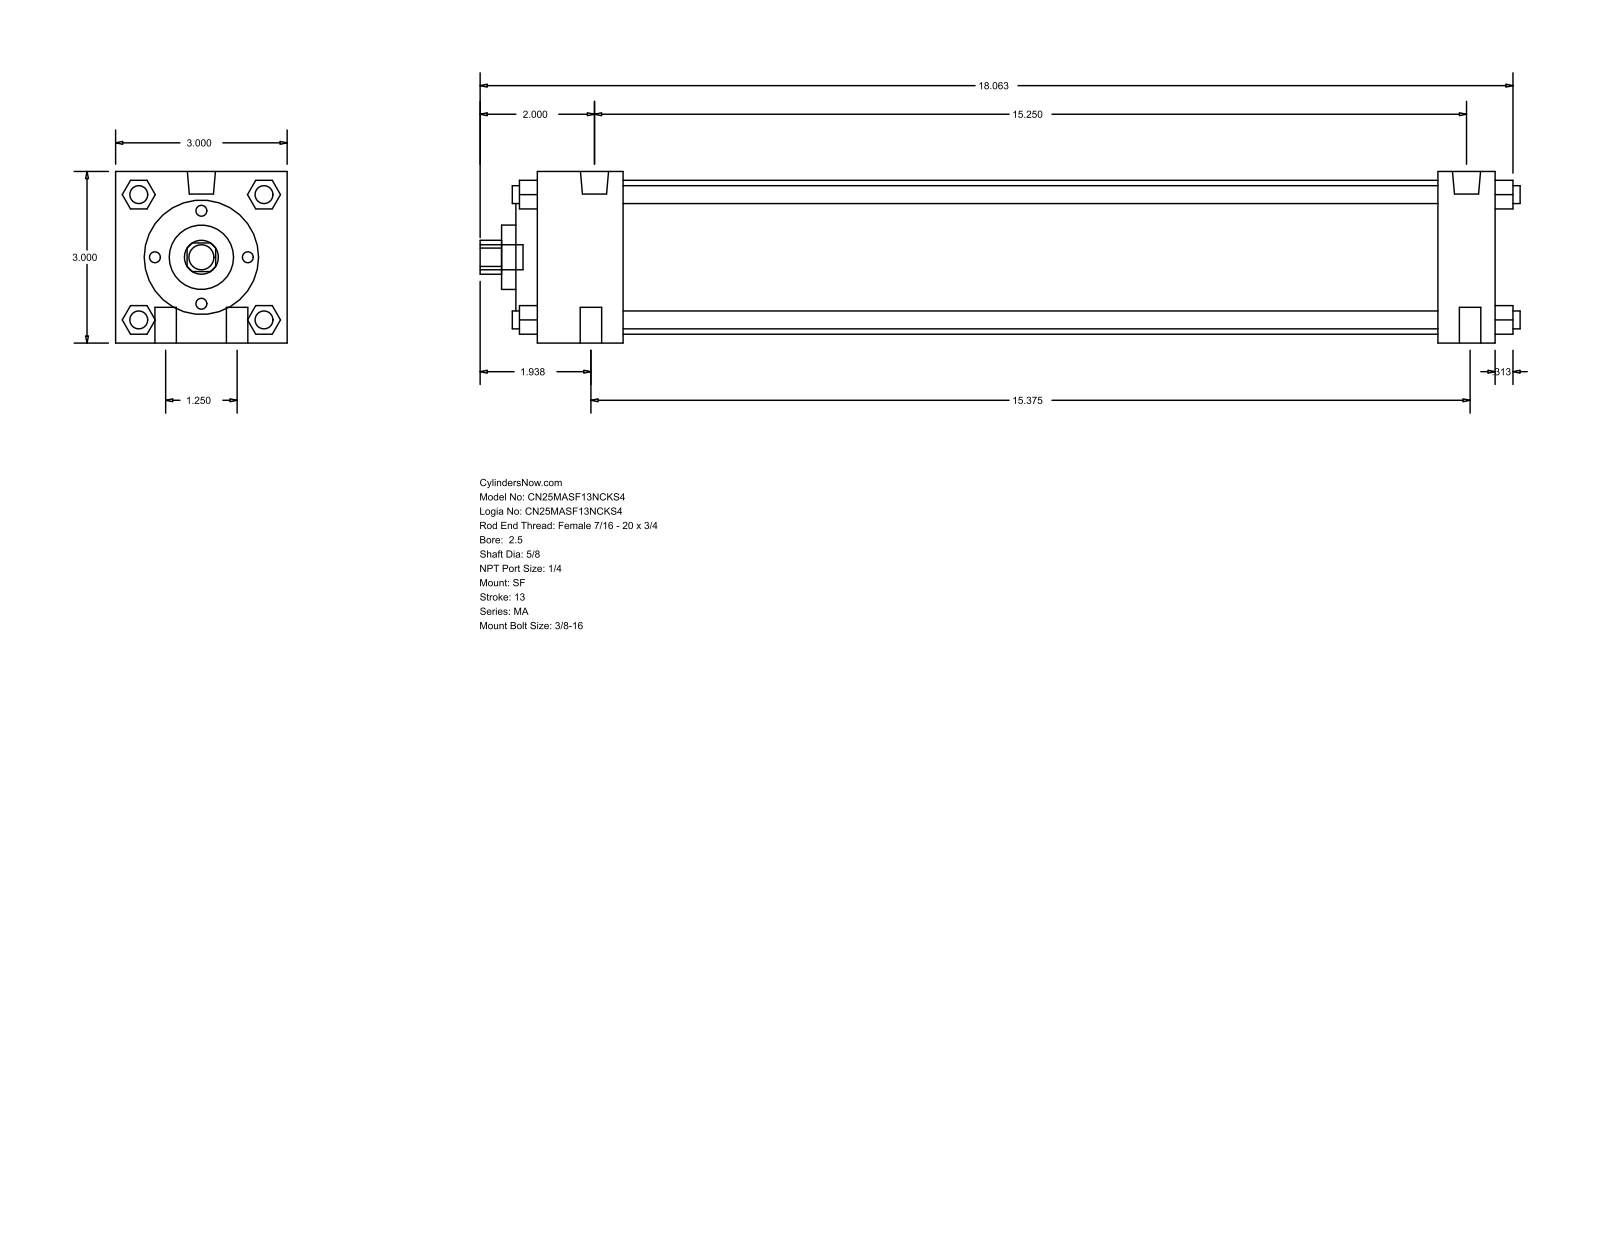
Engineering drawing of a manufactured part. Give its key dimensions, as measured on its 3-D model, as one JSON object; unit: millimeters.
{"part_name": "MA_SF__0250_0.625", "step_written_by": "GSSL Pune (CONFIG_CONTROL_DESIGN)", "units": "millimeters", "bodies": {"solids": 0, "faces": 126, "planar": 95, "cylindrical": 31, "other": 0}, "overall_size": [461.96, 76.2, 76.2], "round_holes": [[15.88, 1], [28.57, 1], [50.8, 1], [68.33, 1]], "round_bosses_or_shafts": [[7.94, 6], [9.53, 4], [12.49, 2], [11.11, 1]], "partial_cylinders_radius": [[7.54, 1]], "face_to_face_distances": [76.2, 425.45, 25.4, 400.05, 38.1, 361.95, 387.35, 12.7, 9.52, 47.62]}
